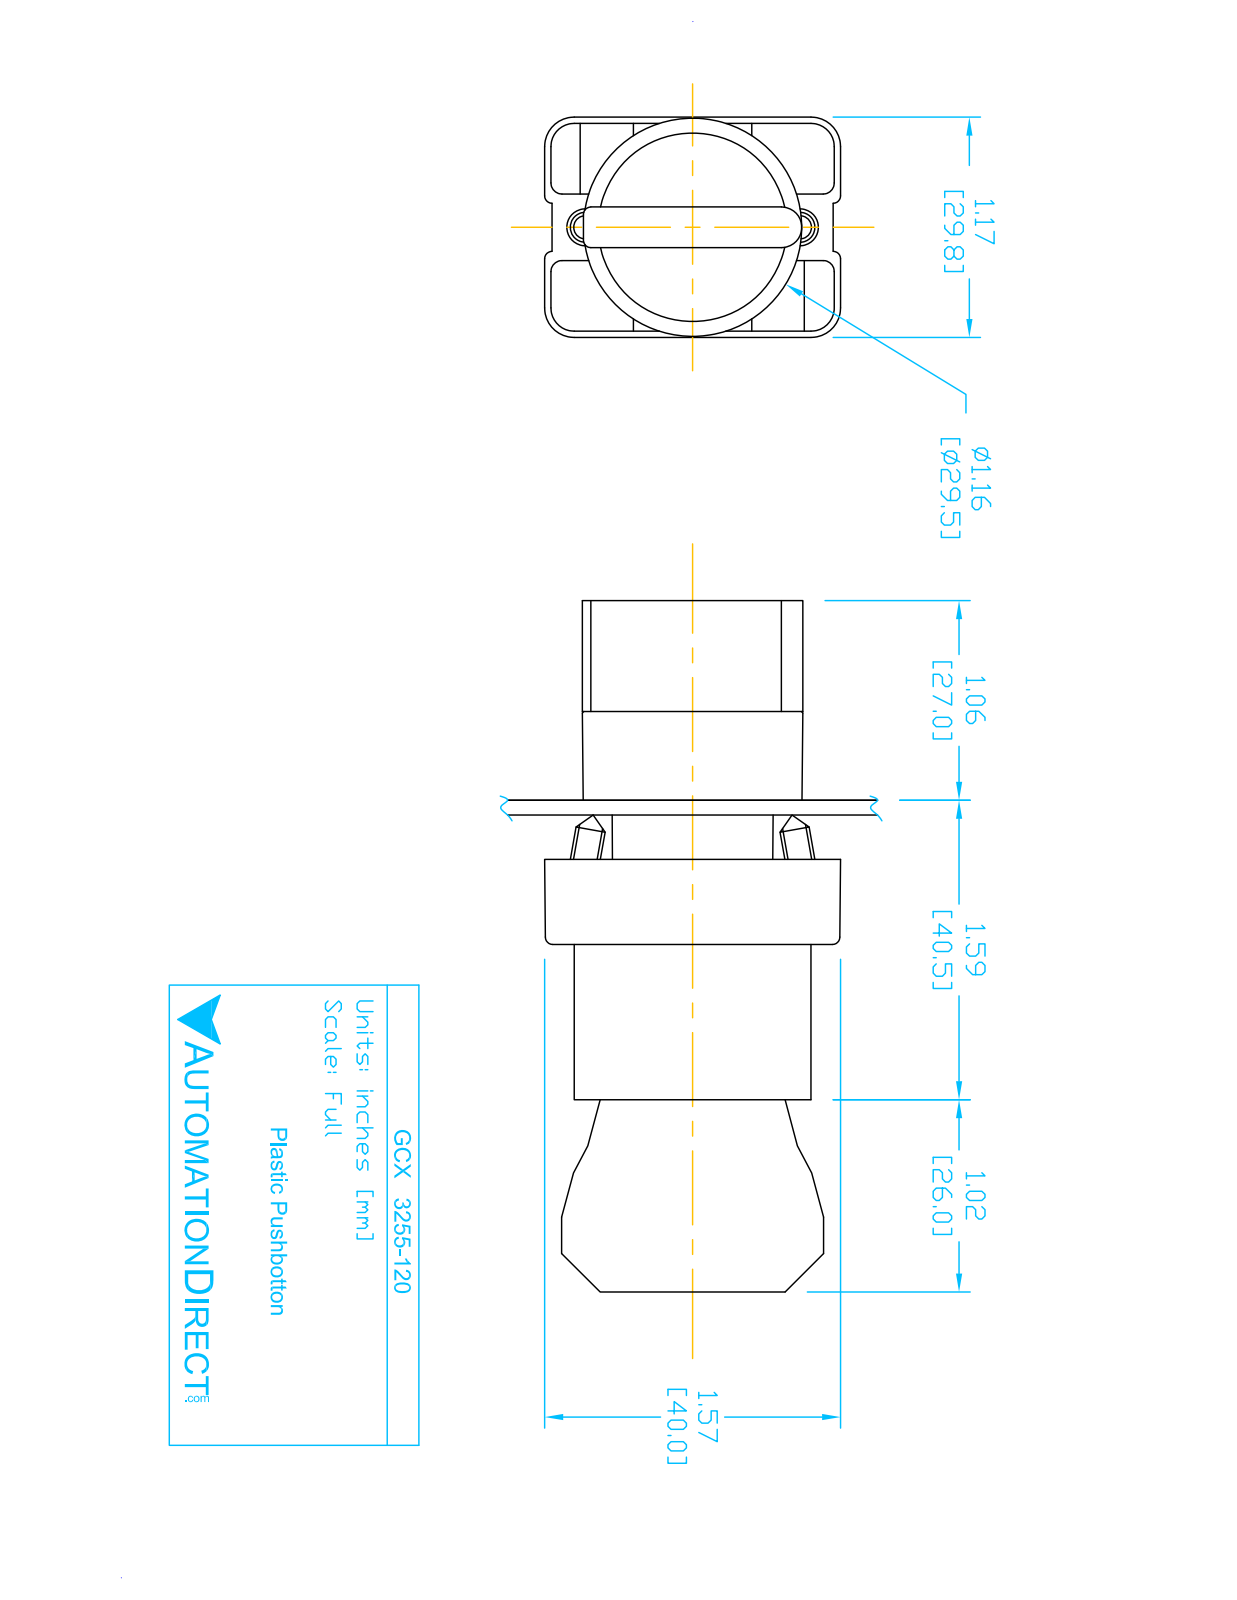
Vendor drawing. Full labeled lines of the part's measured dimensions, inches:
Part name (STEP PRODUCT): GCX3255-120; ecx1040; ECX1050; GCX3255 OPERATOR (+1 more)
STEP written by: SolidWorks 2016 (AUTOMOTIVE_DESIGN)
Units: inches
Bodies: 8 solids, 445 faces (263 planar, 151 cylindrical, 31 other)
Overall size (bounding box): 3.653 × 1.581 × 1.177
Volume: 2.799 in³ · Surface area: 39 in²
Round holes (diameter × count): ⌀0.079 ×2, ⌀0.124 ×2, ⌀0.13 ×2, ⌀0.087 ×1, ⌀0.197 ×1, ⌀0.469 ×1, ⌀0.878 ×1, ⌀0.888 ×1, ⌀1.024 ×1
Round bosses / shafts (diameter × count): ⌀0.157 ×4, ⌀1.175 ×1, ⌀1.004 ×1, ⌀0.945 ×1, ⌀0.856 ×1, ⌀0.78 ×1, ⌀0.504 ×1
Partial cylindrical surfaces — rounded edges, fillets, slot ends (radius × count): R0.059 ×24, R0.041 ×12, R0.124 ×12, R0.157 ×12, R0.039 ×9, R0.128 ×2, R0.02 ×1, R0.063 ×1
Main face-to-face distances: 0.827, 2.02, 1.193, 0.579, 1.244, 1.171, 0.472, 0.469, 0.031, 0.033
Hole centre spacings: 0.236, 0.544, 0.472, 0.49
